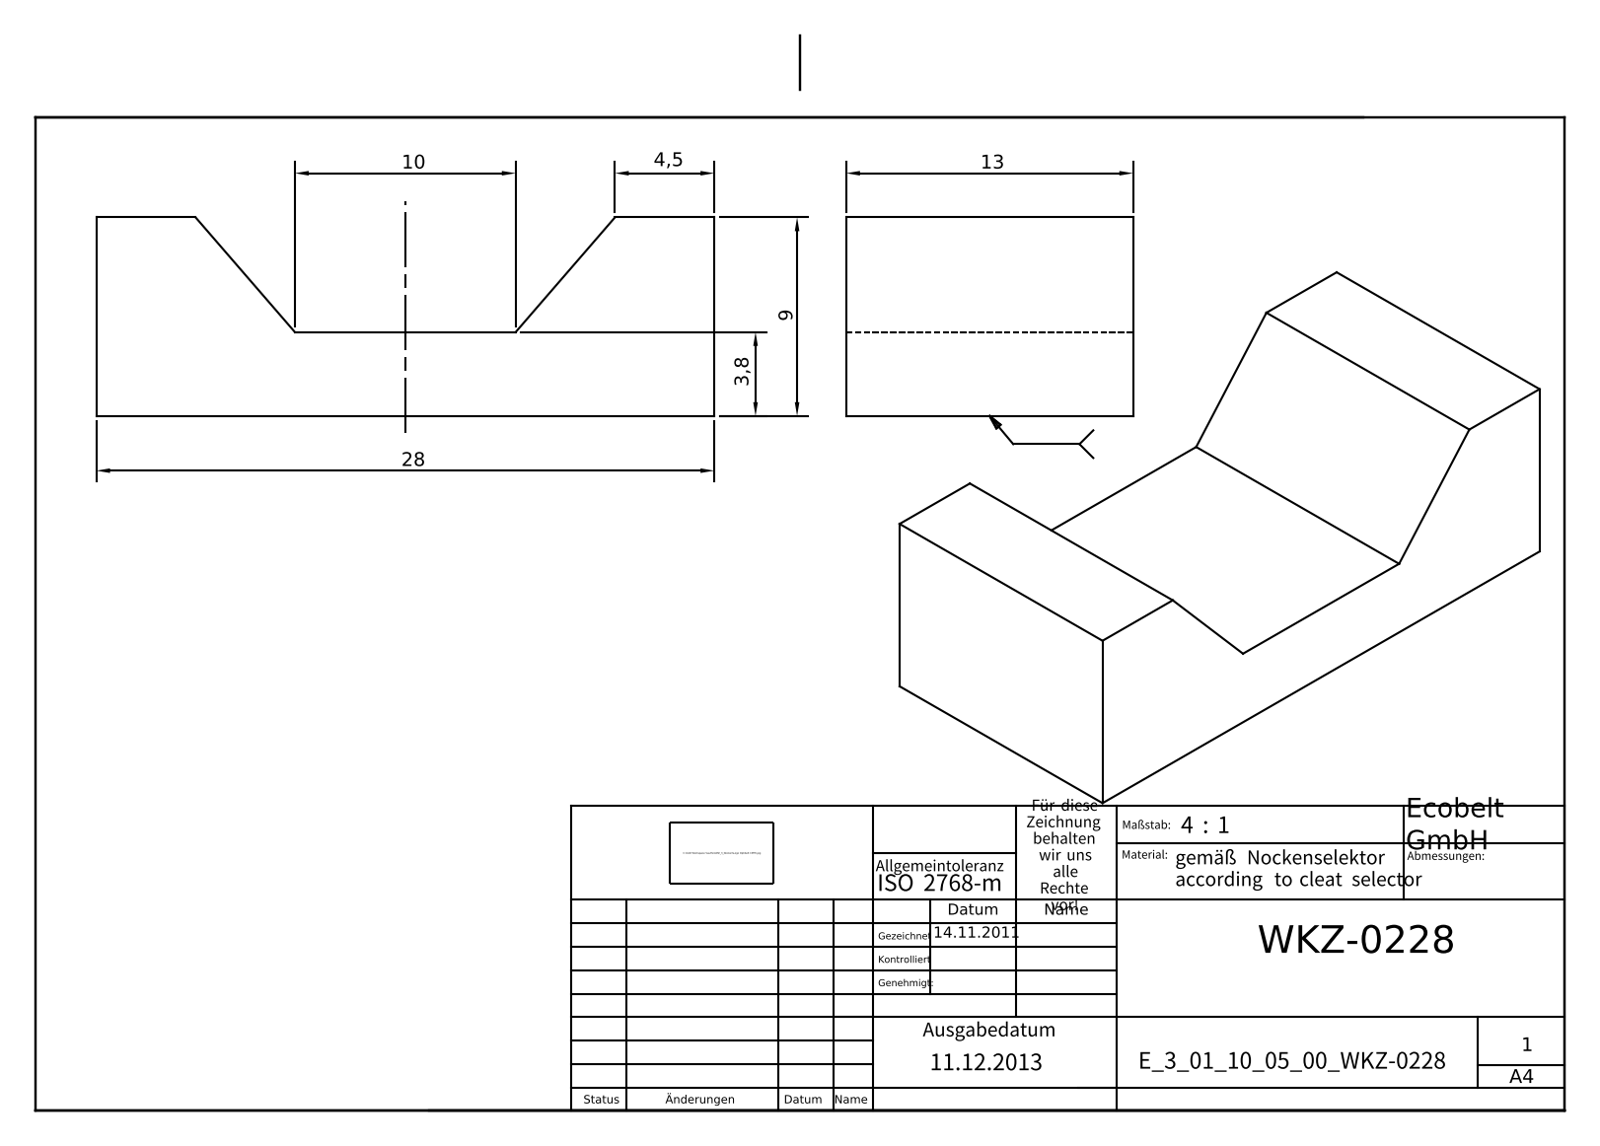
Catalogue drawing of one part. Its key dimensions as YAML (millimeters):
part_name: "E_3_01_10_05_00_WKZ-0228"
step_written_by: "Autodesk Inventor 2025 (AUTOMOTIVE_DESIGN)"
units: millimeters
bodies: {solids: 1, faces: 10, planar: 10, cylindrical: 0, other: 0}
overall_size: [28, 13, 9]
volume: 2296
surface_area: 1377
face_to_face_distances: [13, 3.8, 28, 9, 5.2]
